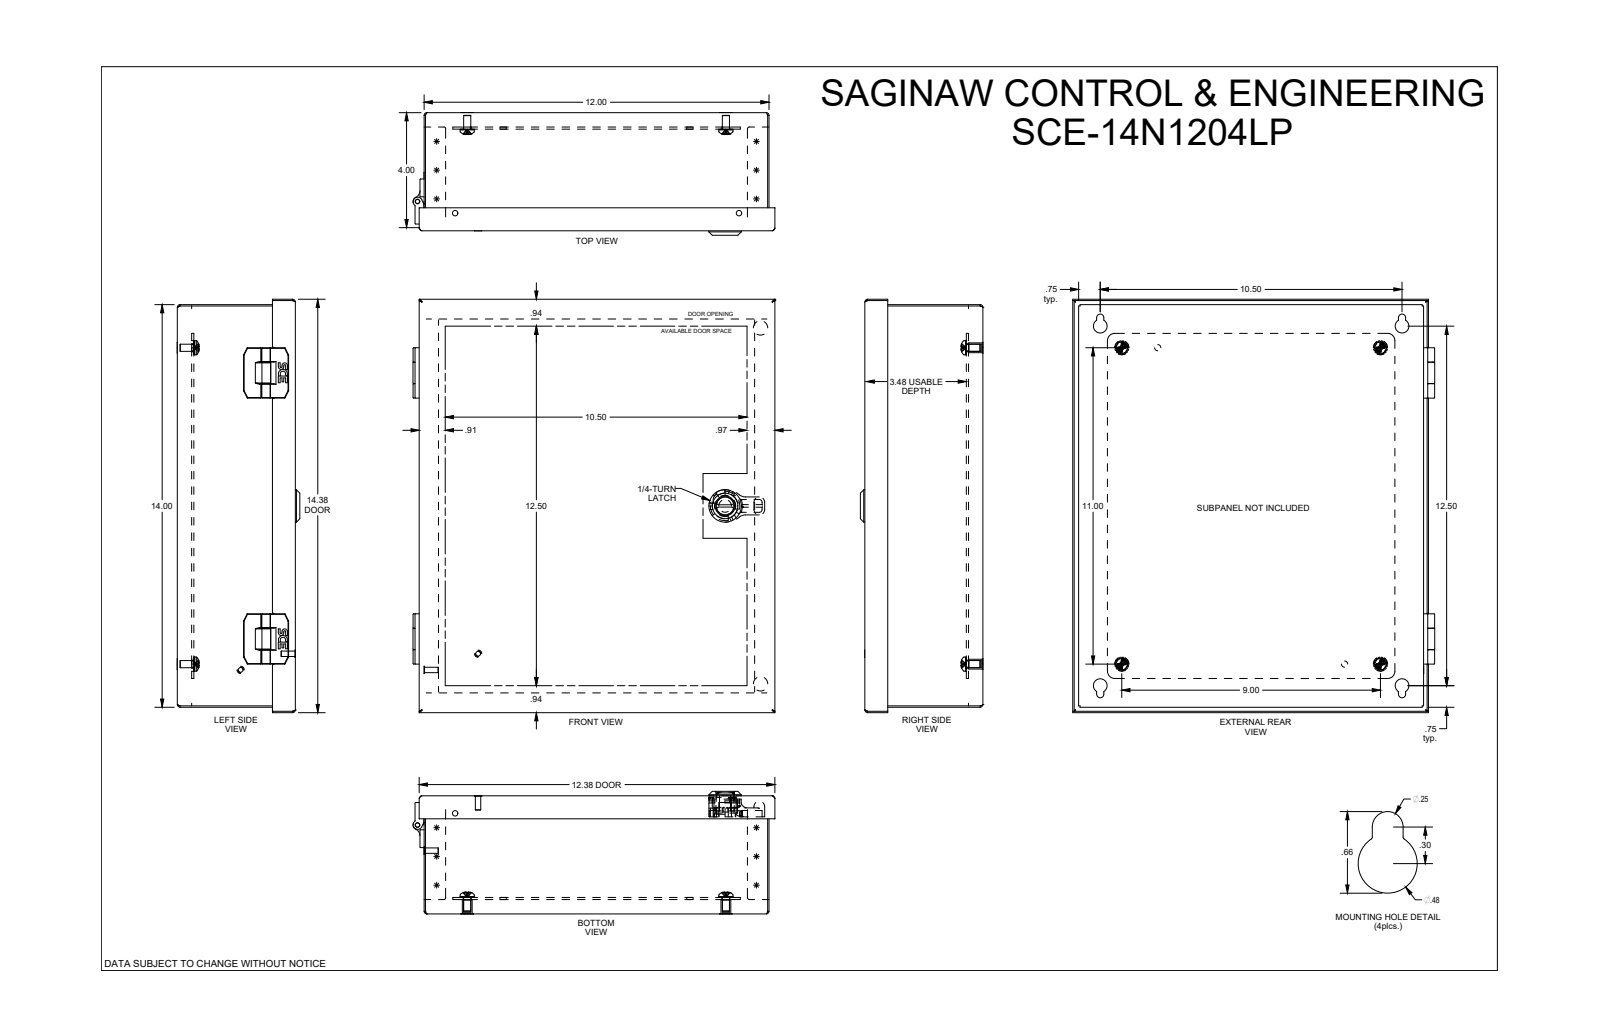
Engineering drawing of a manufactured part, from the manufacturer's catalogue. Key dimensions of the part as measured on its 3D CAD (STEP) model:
Part name (STEP PRODUCT): SCE-14N1204LP
STEP written by: SolidWorks 2019 (AUTOMOTIVE_DESIGN)
Units: inches
Bodies: 31 solids, 1545 faces (578 planar, 643 cylindrical, 324 other)
Overall size (bounding box): 14.375 × 12.593 × 4.267
Volume: 47.44 in³ · Surface area: 1 511 in²
Round holes (diameter × count): ⌀0.17 ×4, ⌀0.25 ×4, ⌀0.281 ×4, ⌀0.329 ×4, ⌀0.343 ×4, ⌀0.48 ×4, ⌀0.193 ×3, ⌀0.187 ×2, ⌀0.218 ×2, ⌀0.158 ×1, ⌀0.44 ×1, ⌀0.635 ×1
Round bosses / shafts (diameter × count): ⌀0.492 ×4, ⌀0.479 ×4, ⌀0.341 ×4, ⌀0.248 ×4, ⌀0.237 ×4, ⌀0.16 ×4, ⌀0.5 ×2, ⌀0.323 ×2
Partial cylindrical surfaces — rounded edges, fillets, slot ends (radius × count): R0.01 ×253, R0.02 ×95, R0.06 ×25, R0.015 ×24, R0.025 ×24, R0.055 ×6, R0.25 ×6, R0.125 ×4
Main face-to-face distances: 0.06, 4.047, 3.987, 4.107, 0.5, 0.44, 0.575, 0.515, 3.472, 3.532
Hole centre spacings: 1.061, 7.75, 9.779, 11.774, 15.269, 1.089, 1.091, 9.25
